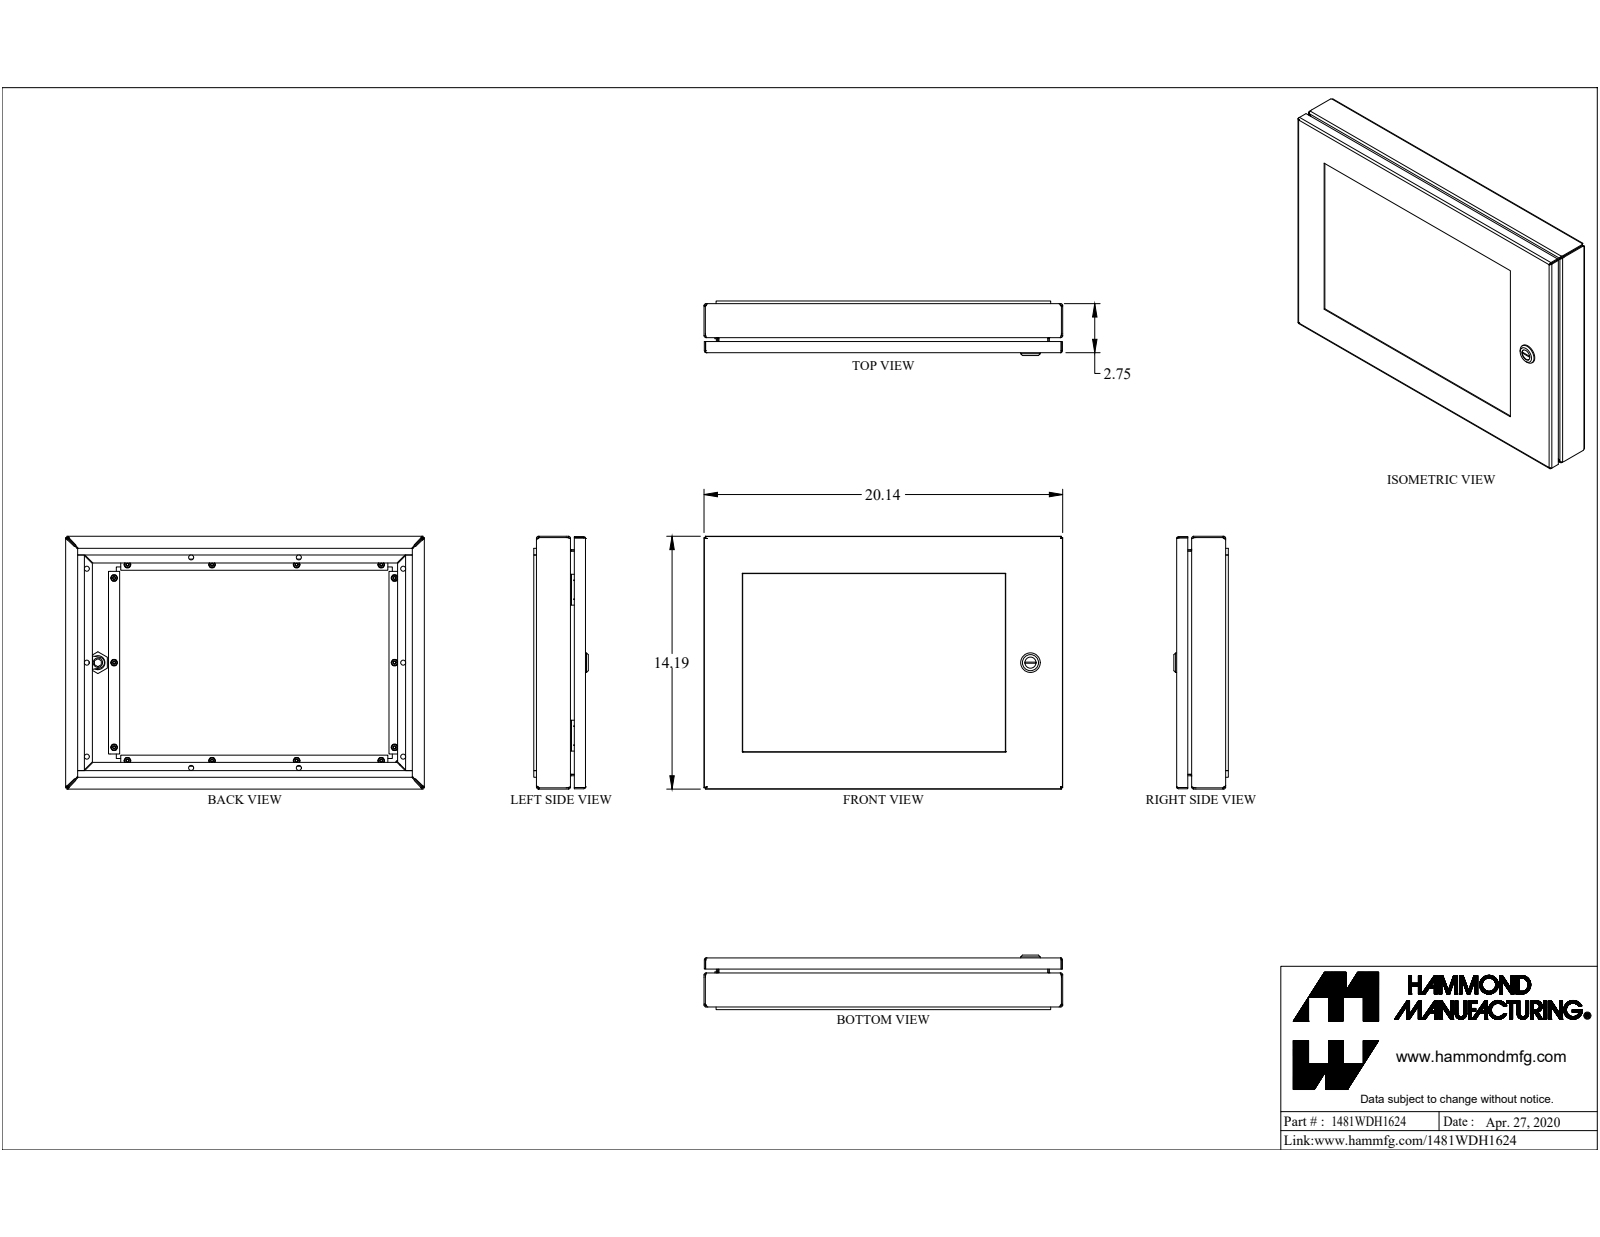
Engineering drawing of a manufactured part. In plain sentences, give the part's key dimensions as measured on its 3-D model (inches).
The part is named "1481WDH1624". Its 3-D file was written by "SolidWorks 2019 (CONFIG_CONTROL_DESIGN)". It is 60 solids with 1087 faces: 657 planar, 248 cylindrical and 182 other. Overall it measures 20.14 by 14.19 by 3.061 inches. Its volume is 91.8 cubic inches and its surface area 1 723 square inches. Round holes: 14 of diameter 0.13, 14 of diameter 0.25, 10 of diameter 0.281, 1 of diameter 0.172, 1 of diameter 0.232, 1 of diameter 0.24, 1 of diameter 0.242, 1 of diameter 0.625, 1 of diameter 0.785. Round bosses or shafts: 15 of diameter 0.226, 14 of diameter 0.368, 14 of diameter 0.164, 1 of diameter 1.1, 1 of diameter 0.525, 1 of diameter 0.455, 1 of diameter 0.455, 1 of diameter 0.398. Partial cylindrical surfaces (rounded edges, fillets, slot ends): 28 of radius 0.036, 28 of radius 0.108, 12 of radius 0.382, 8 of radius 19.003, 4 of radius 0.006, 4 of radius 0.016, 4 of radius 0.062, 4 of radius 0.088. The main face-to-face distances are 0.072, 0.25, 0.215, 0.035, 0.037, 0.287, 2.579, 2.614, 0.843, 1.736. The hole center spacings are 4.75, 15.75, 5.551, 10.278, 11.633, 14.496, 15.019, 16.451.
